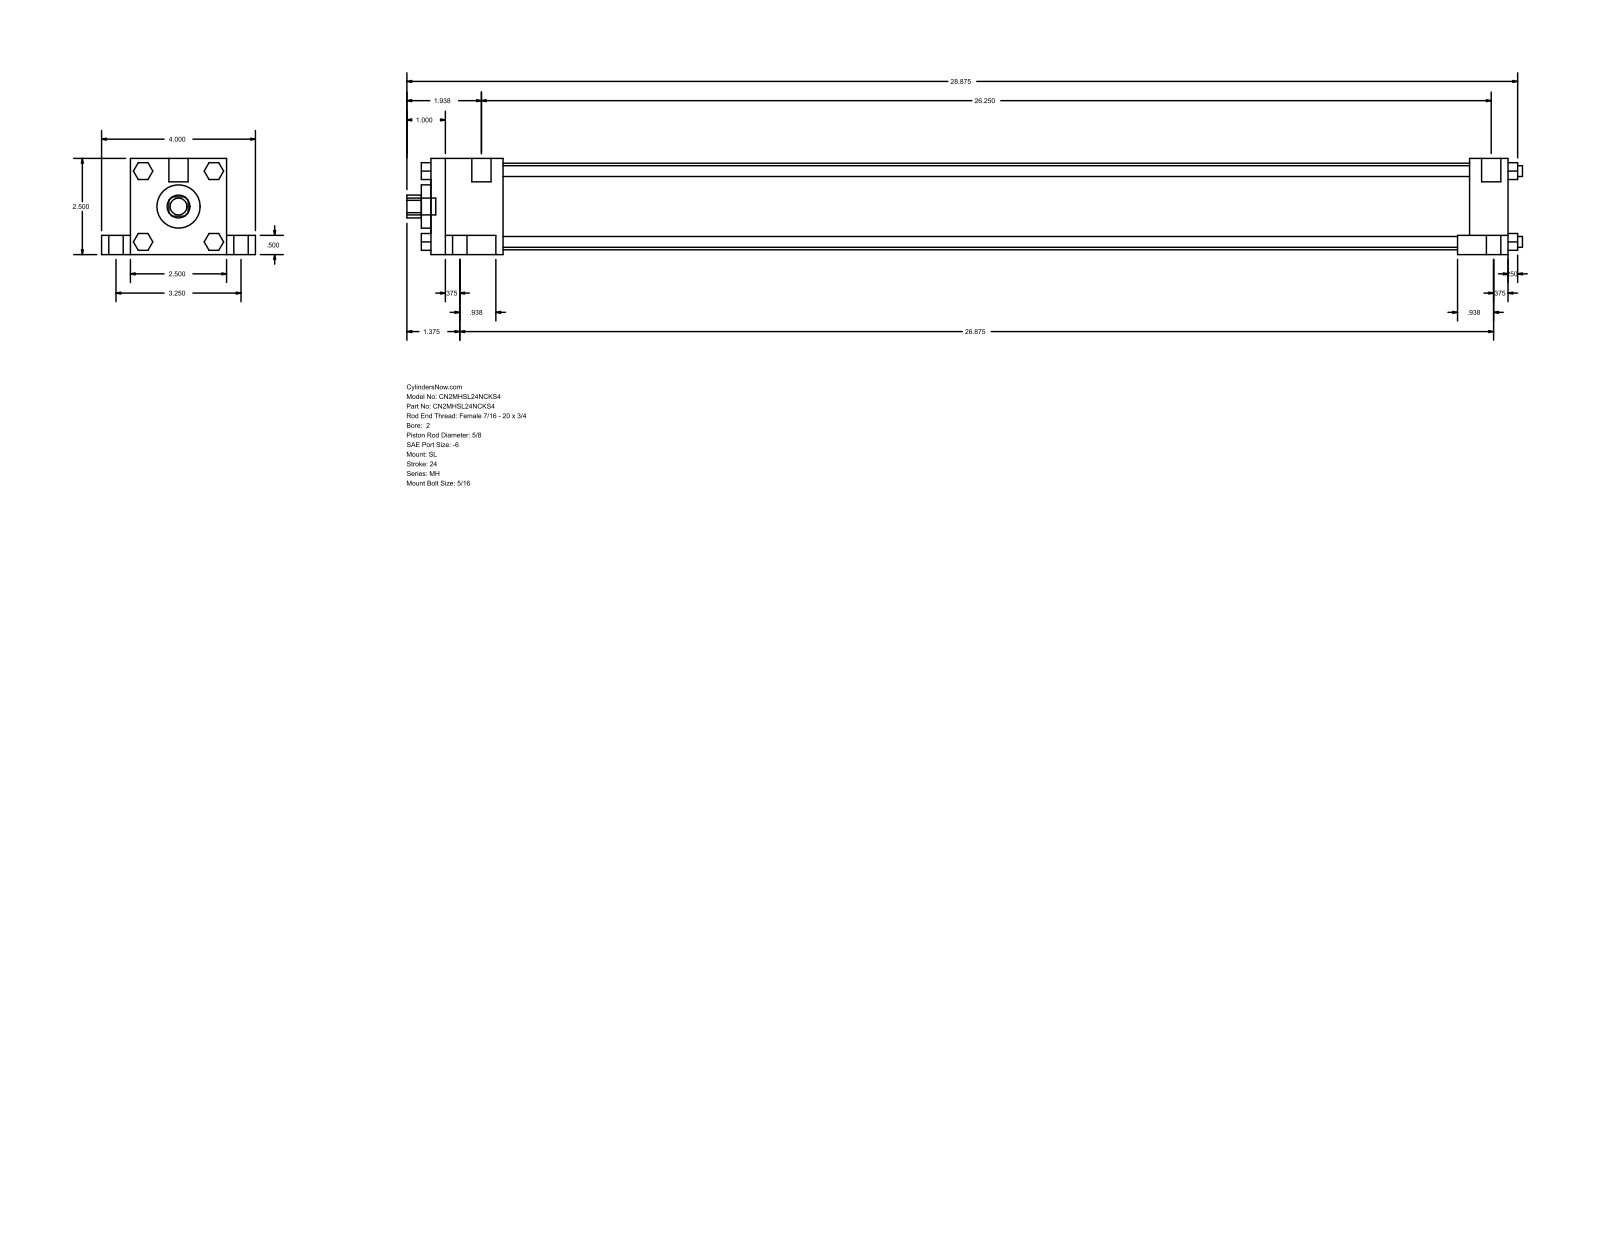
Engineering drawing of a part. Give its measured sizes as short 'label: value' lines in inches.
name: MH_SL__0200_0.625
written by: GSSL Pune (CONFIG_CONTROL_DESIGN)
unit: in
bodies: 0 solids, 148 faces (112 planar, 36 cylindrical, 0 other)
size: 29 × 4 × 2.5
holes: 1× ⌀0.625, 1× ⌀1.125, 1× ⌀2.25
bosses: 4× ⌀0.625, 4× ⌀0.375, 4× ⌀0.281, 4× ⌀0.219, 2× ⌀0.5, 1× ⌀0.437
rounds: 1× R0.297
face distances: 2.5, 28, 0.5, 0.75, 2, 3.25, 27, 1, 1.875, 25.125
